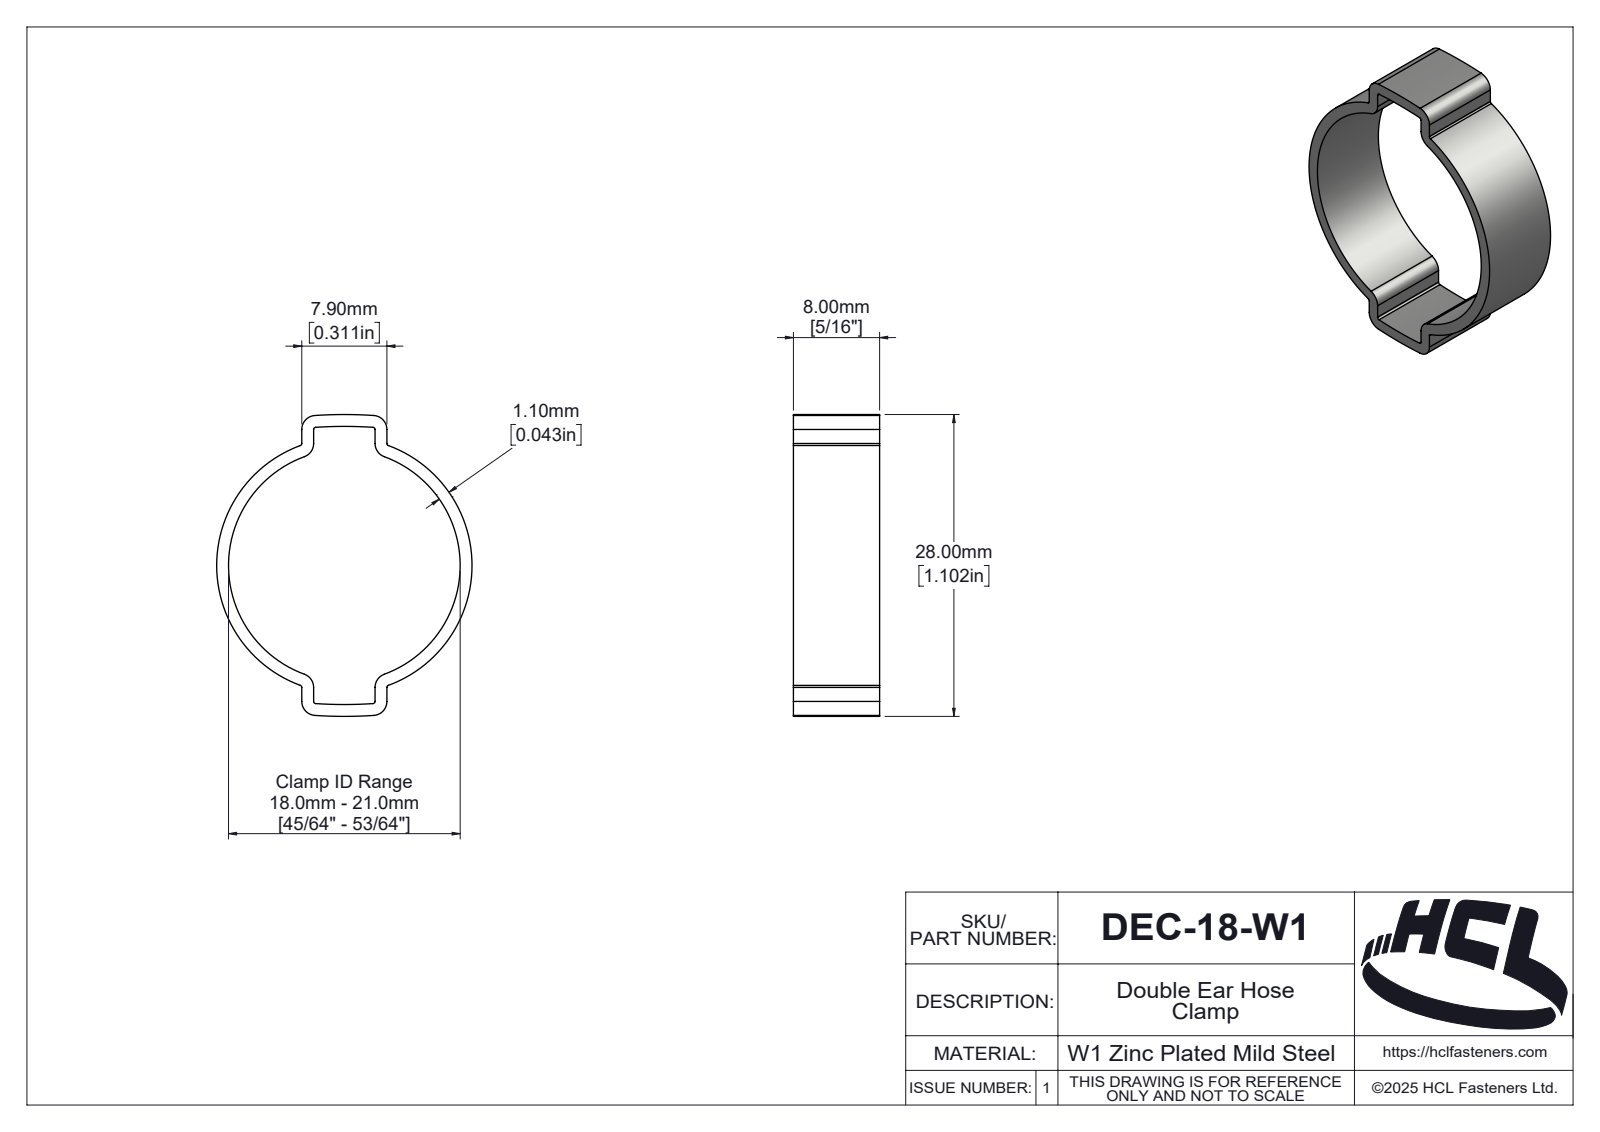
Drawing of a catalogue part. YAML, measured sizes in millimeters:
part_name: "DEC-18-W1"
step_written_by: "SolidWorks 2025 (AUTOMOTIVE_DESIGN)"
units: millimeters
bodies: {solids: 1, faces: 137, planar: 12, cylindrical: 67, other: 58}
overall_size: [28, 23.7, 8]
volume: 697
surface_area: 1447
partial_cylinders:
  - {radius: 0.2, count: 8}
  - {radius: 1.3, count: 8}
  - {radius: 40.66, count: 2}
  - {radius: 41.76, count: 2}
  - {radius: 0.2, count: 1}
  - {radius: 0.81, count: 1}
  - {radius: 1.01, count: 1}
  - {radius: 1.06, count: 1}
face_to_face_distances: [8, 1.1, 6.8, 7.9, 5.7, 3.83, 2.73, 2.97, 4.07, 3.68]
